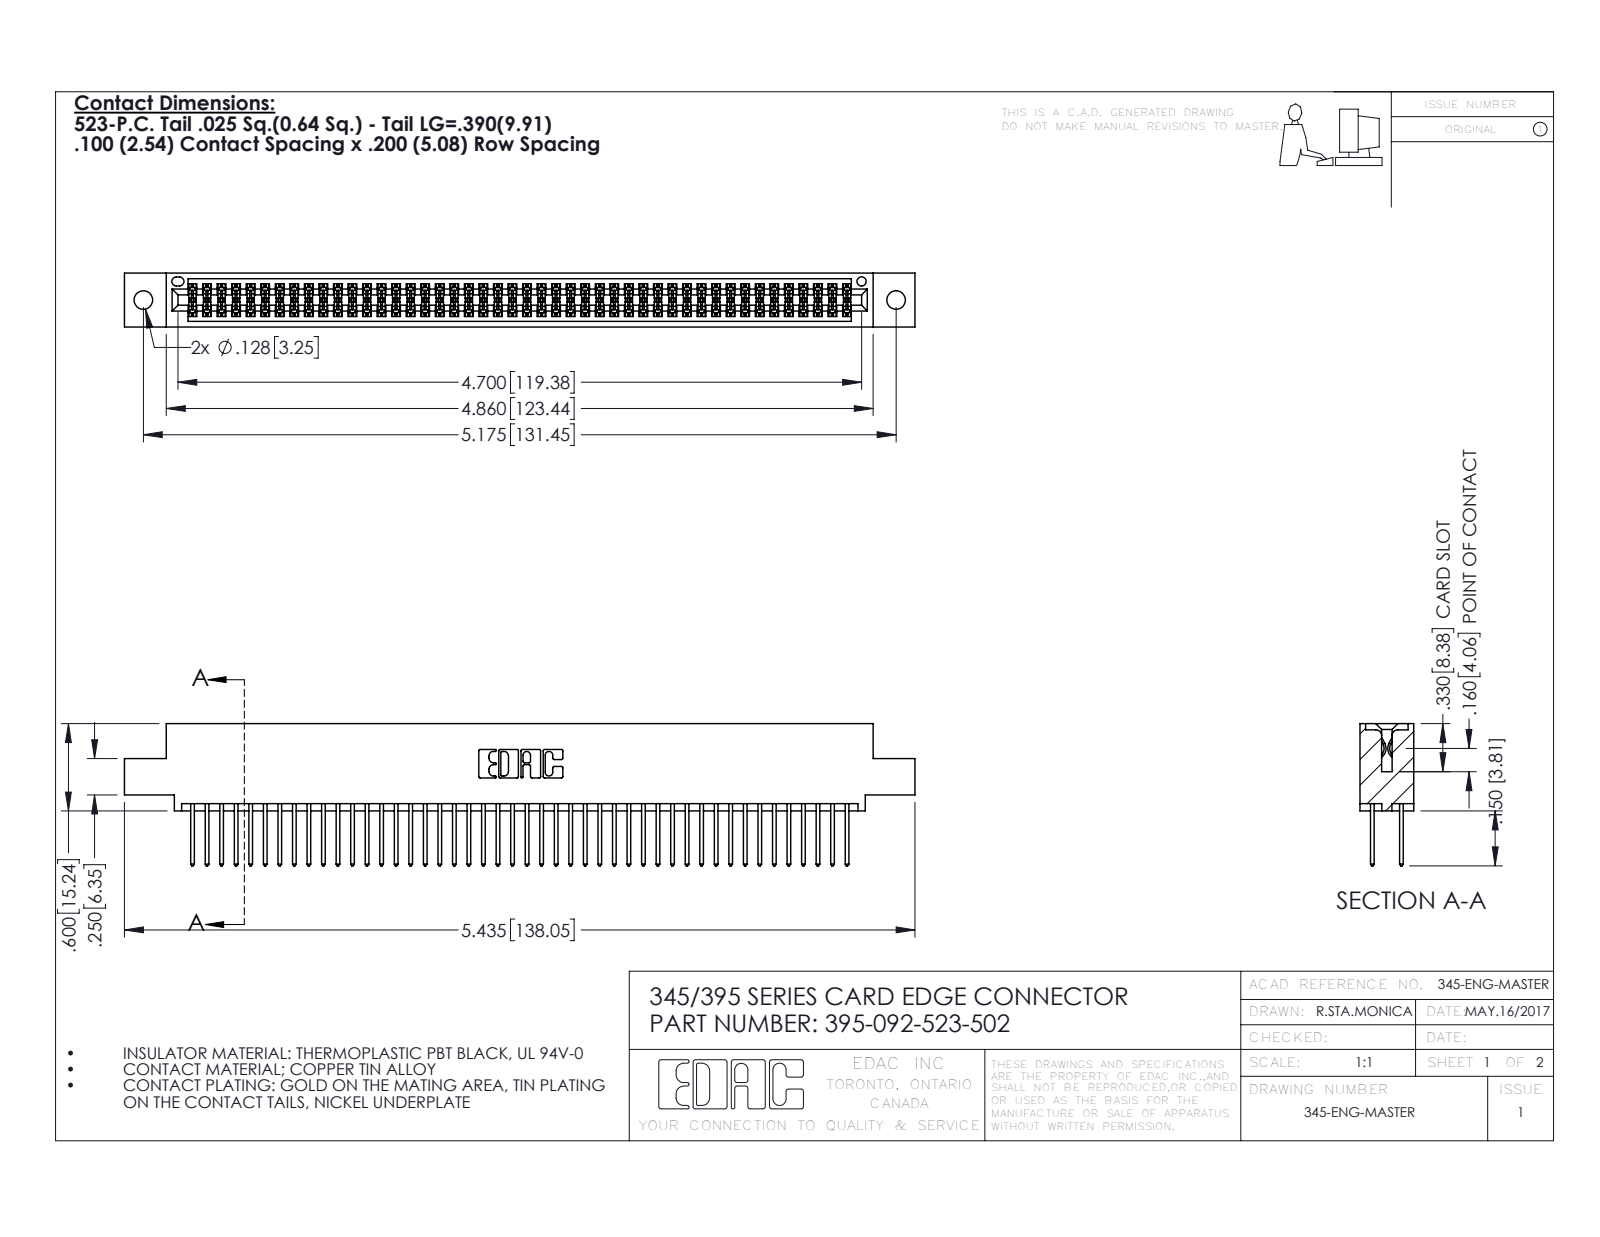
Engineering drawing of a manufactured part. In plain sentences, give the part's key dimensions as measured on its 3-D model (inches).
The part is named "395-092-523-502; 345 Part_0.110 Offset - 0.128 Dia; 345-292-001_345-293-123". Its 3-D file was written by "SolidWorks 2016 (CONFIG_CONTROL_DESIGN)". It is 93 solids with 4730 faces: 3120 planar, 1610 cylindrical and 0 other. Overall it measures 5.435 by 0.977 by 0.37 inches. Its volume is 0.825 cubic inches and its surface area 32.14 square inches. Round holes: 2 of diameter 0.128, 1 of diameter 0.064. Partial cylindrical surfaces (rounded edges, fillets, slot ends): 138 of radius 0.006, 92 of radius 0.01, 22 of radius 0.01, 6 of radius 0.007, 6 of radius 0.031, 3 of radius 0.026, 2 of radius 0.014, 2 of radius 0.019. The main face-to-face distances are 0.298, 0.072, 0.2, 0.098, 0.272, 0.025, 0.37, 0.225, 0.175, 0.149. The hole center spacings are 0.27, 4.939, 5.175.
